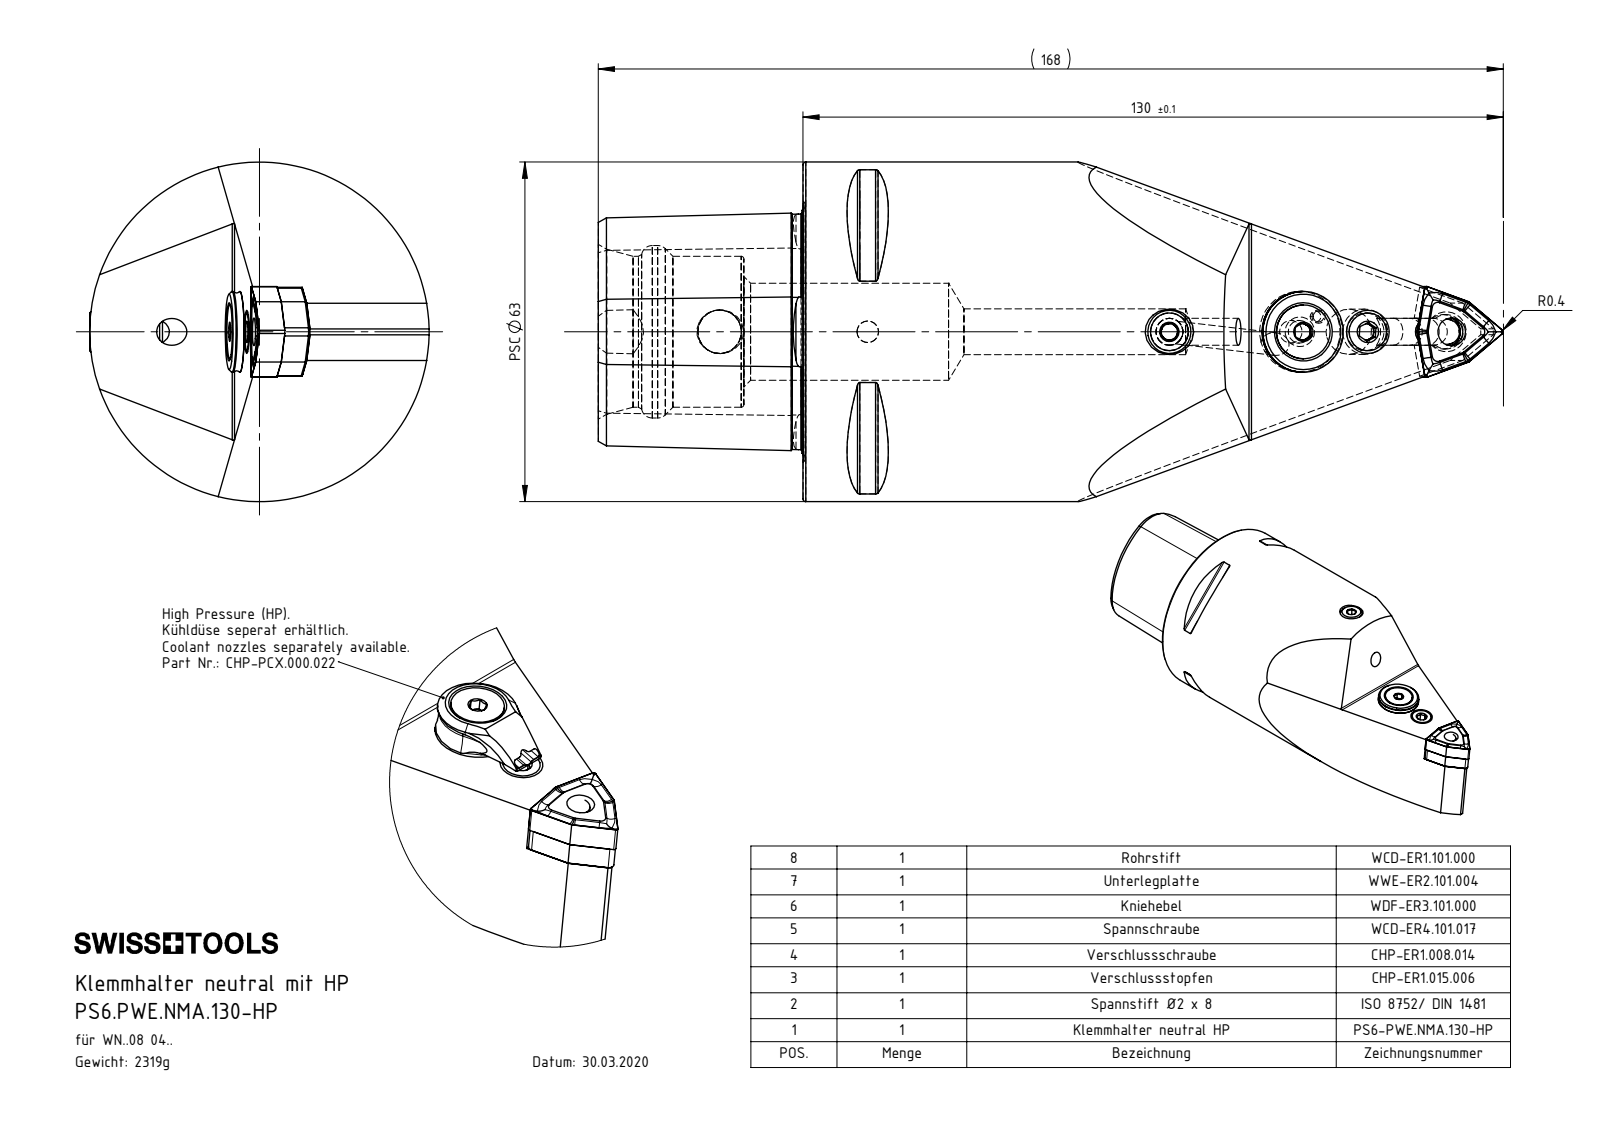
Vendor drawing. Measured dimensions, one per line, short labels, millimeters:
name: PS6-PWE.NMA.130-HP_A; WCD-ER1.101.000; WWE-ER2.101.004_A; CHP-ER1.008.014_A (+8 more)
written by: SolidWorks 2017 (AUTOMOTIVE_DESIGN)
unit: mm
bodies: 11 solids, 333 faces (137 planar, 66 cylindrical, 130 other)
size: 168 × 63 × 63
volume: 295 232 mm³; area: 43 033 mm²
holes: 2× ⌀4.2, 2× ⌀5, 2× ⌀7, 1× ⌀1.2, 1× ⌀2, 1× ⌀2.5, 1× ⌀3, 1× ⌀4, 1× ⌀5.16, 1× ⌀5.2, 1× ⌀6.7, 1× ⌀7.8
bosses: 2× ⌀8, 1× ⌀63, 1× ⌀15, 1× ⌀13.4, 1× ⌀10, 1× ⌀7.9, 1× ⌀6.4, 1× ⌀5.5
rounds: 9× R0.5, 3× R0.4, 3× R1, 3× R2.5, 2× R3.2, 1× R2.3, 1× R2.35, 1× R2.8
face distances: 38, 24.88, 4.47, 4.53, 27, 11, 4.7, 55.8, 4.76, 4.85
hole spacings: 4.51, 4.49, 4.53, 9.14, 9.17, 12.22, 12.25, 15.61
